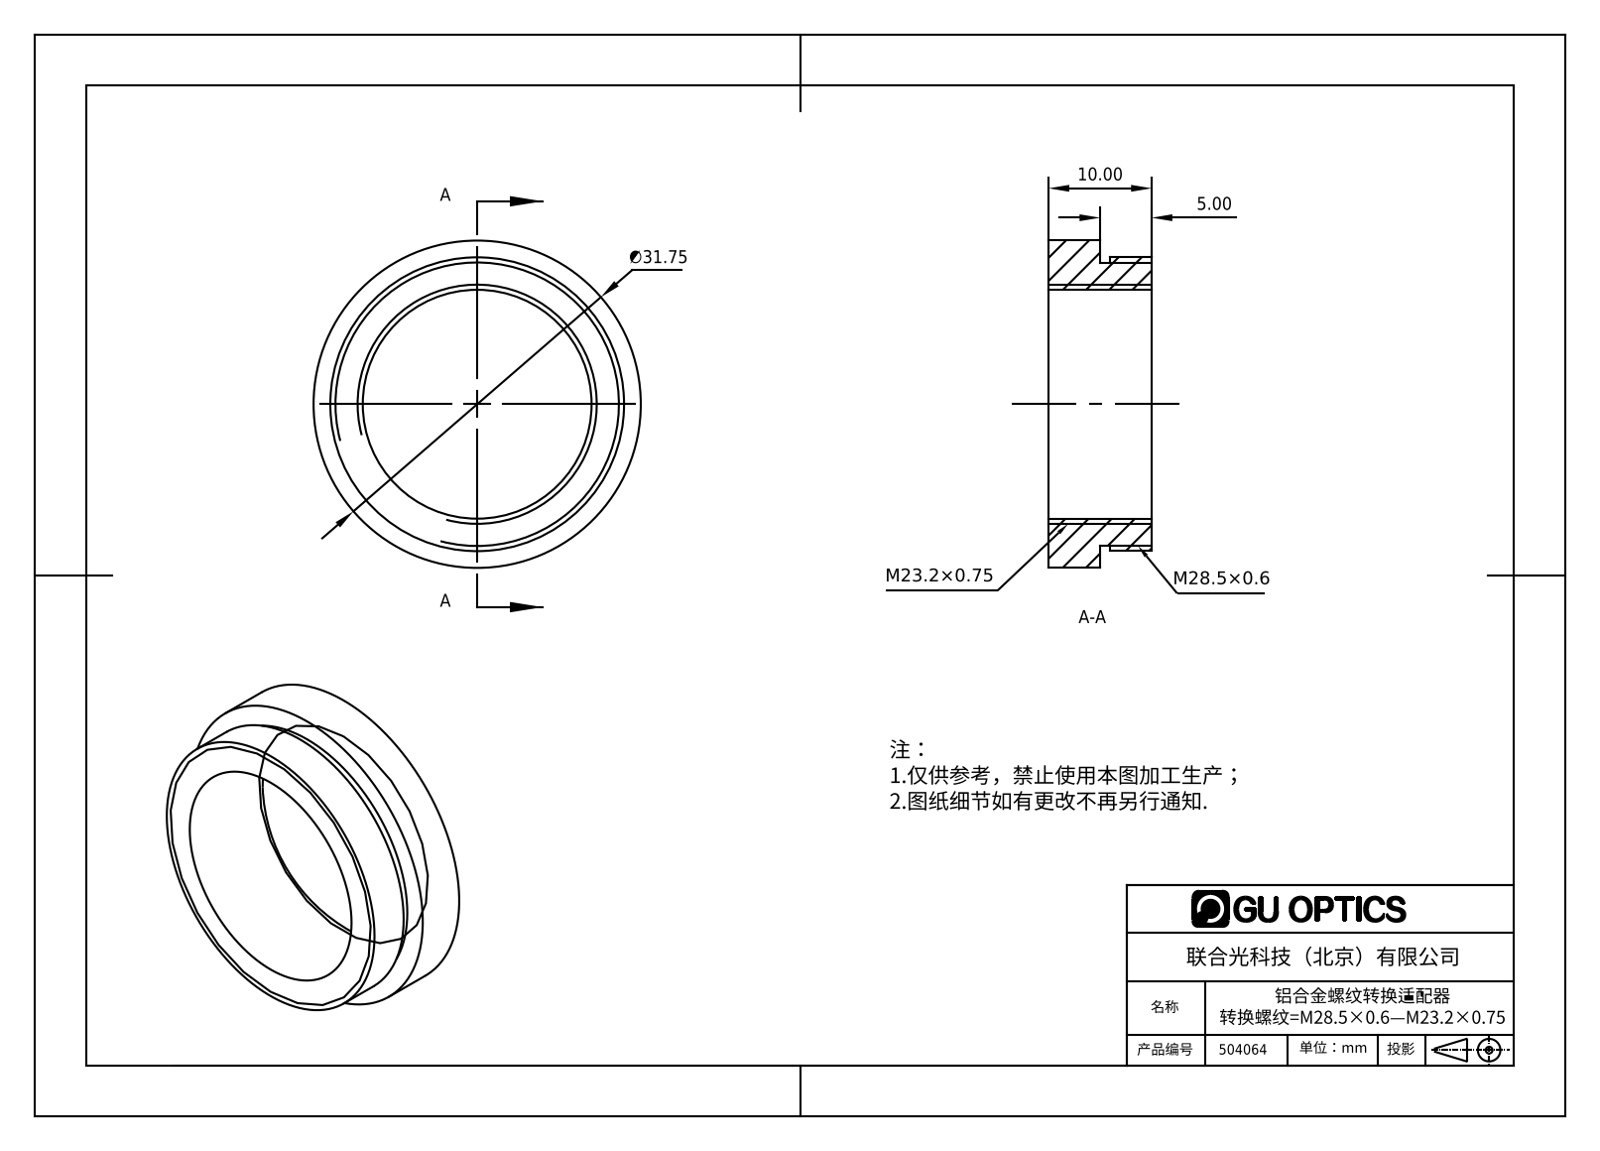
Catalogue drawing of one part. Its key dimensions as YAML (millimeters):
part_name: "504064"
step_written_by: "SolidWorks 2016 (AUTOMOTIVE_DESIGN)"
units: millimeters
bodies: {solids: 1, faces: 12, planar: 4, cylindrical: 8, other: 0}
overall_size: [31.75, 31.75, 10]
volume: 3234
surface_area: 2538
round_holes:
  - {diameter: 22.2, count: 1}
round_bosses_or_shafts:
  - {diameter: 31.75, count: 1}
  - {diameter: 28.5, count: 1}
  - {diameter: 27.5, count: 1}
face_to_face_distances: [5, 10, 6, 1, 4]
